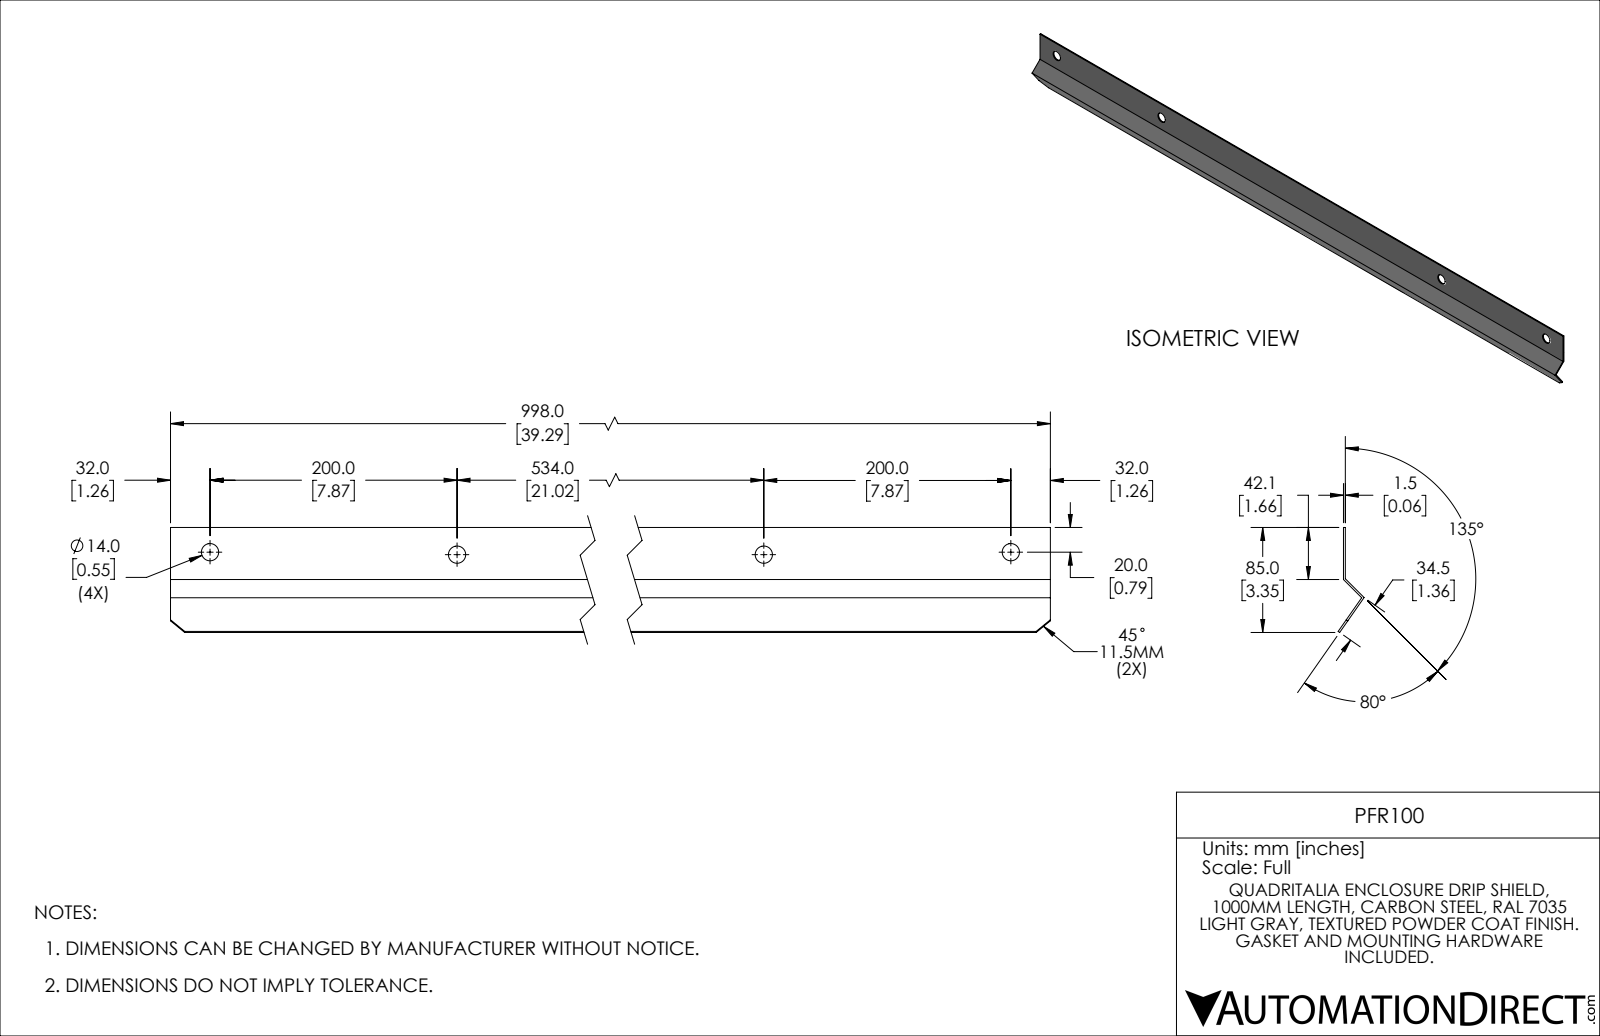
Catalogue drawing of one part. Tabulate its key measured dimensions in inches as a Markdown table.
| quantity | value |
| --- | --- |
| part name | PFR100 |
| STEP written by | SolidWorks 2021 (CONFIG_CONTROL_DESIGN) |
| units | inches |
| bodies | 1 solid, 16 faces (12 planar, 4 cylindrical, 0 other) |
| overall size | 39.291 × 3.345 × 0.827 |
| volume | 8.78 in³ |
| surface area | 302.8 in² |
| round holes (diameter × count) | 0.551 × 4 |
| main face-to-face distances | 0.059, 39.291 |
| hole center spacings | 7.874, 28.898, 21.024, 36.772 |
